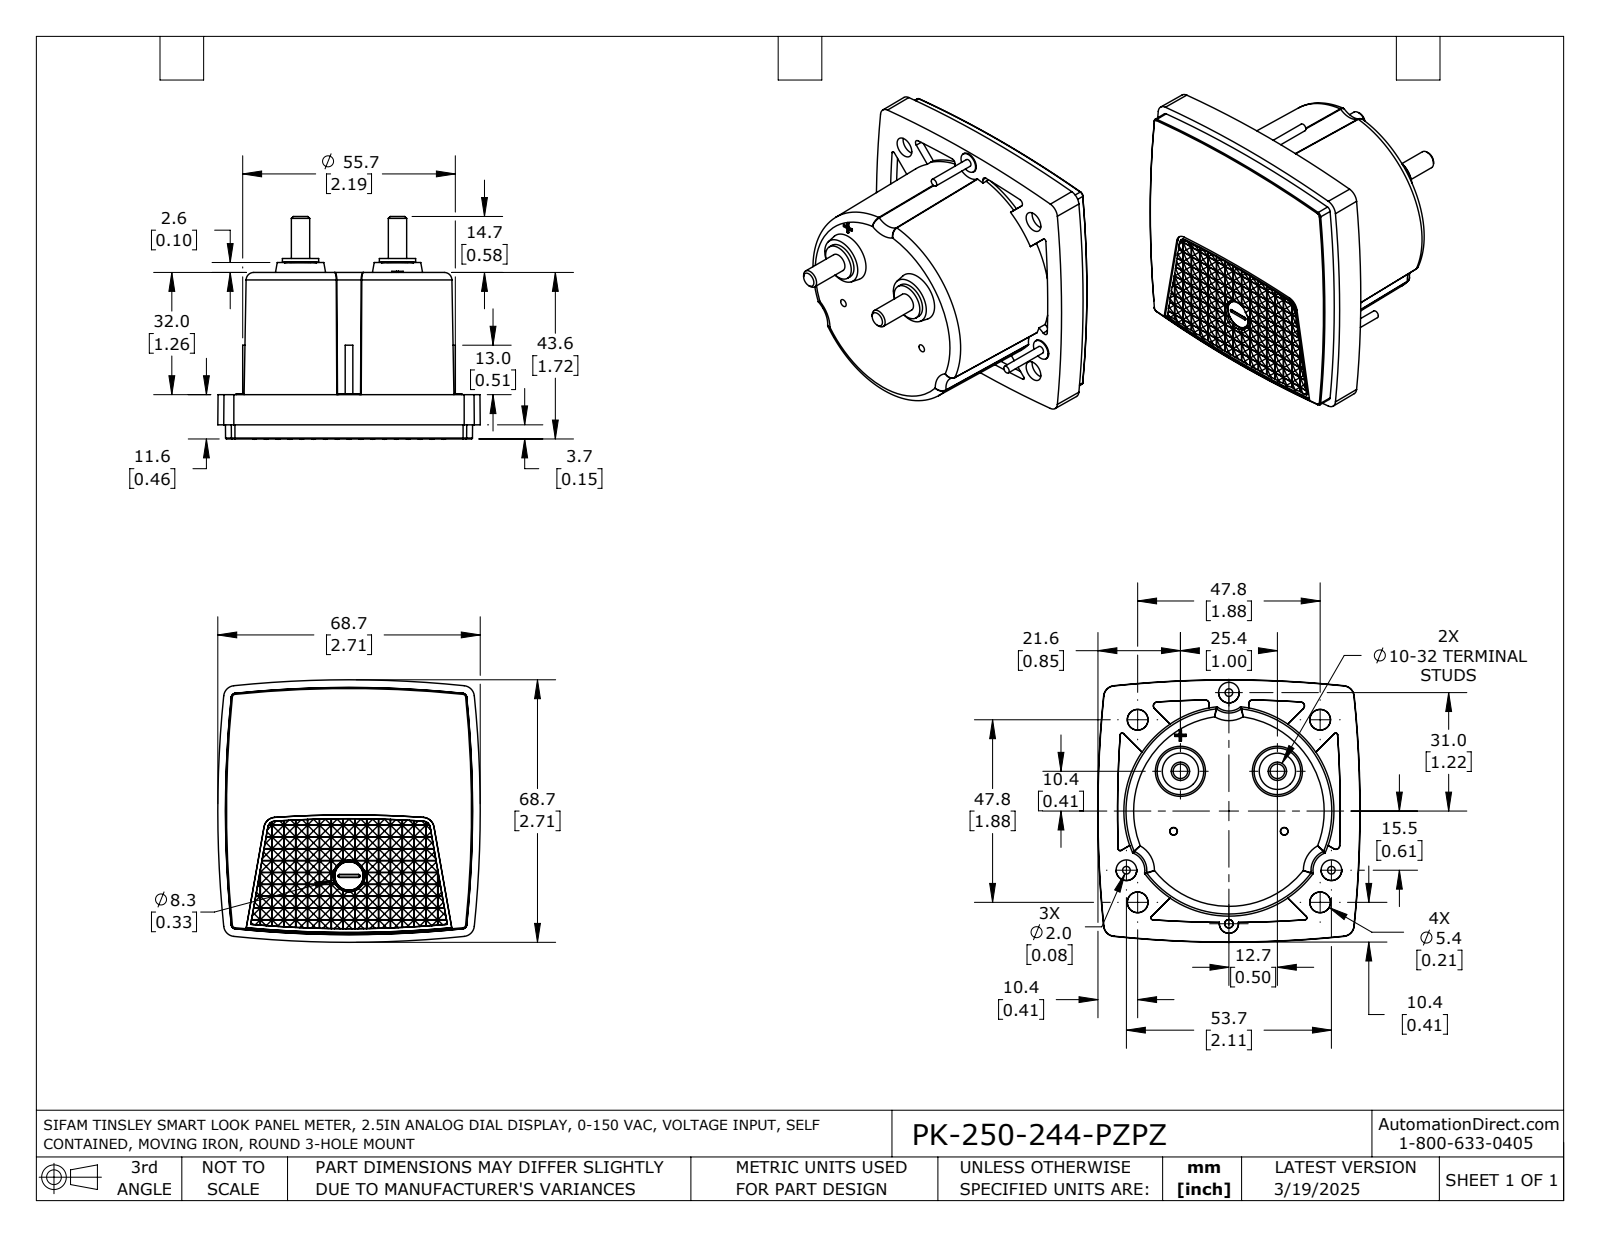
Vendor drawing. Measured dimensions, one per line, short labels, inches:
name: PK-250-244-PZPZ
written by: SolidWorks 2021 (AUTOMOTIVE_DESIGN)
unit: in
bodies: 1 solid, 1550 faces (1165 planar, 265 cylindrical, 120 other)
size: 2.706 × 2.706 × 2.297
volume: 7.594 in³; area: 30.41 in²
bosses: 3× ⌀0.213, 3× ⌀0.079, 2× ⌀0.374, 2× ⌀0.189, 1× ⌀0.215
rounds: 2× R0.167, 1× R1.083
face distances: 1.717, 1.26, 0.457, 0.024, 0.087, 0.096, 0.311, 0.12, 0.072, 1.346
